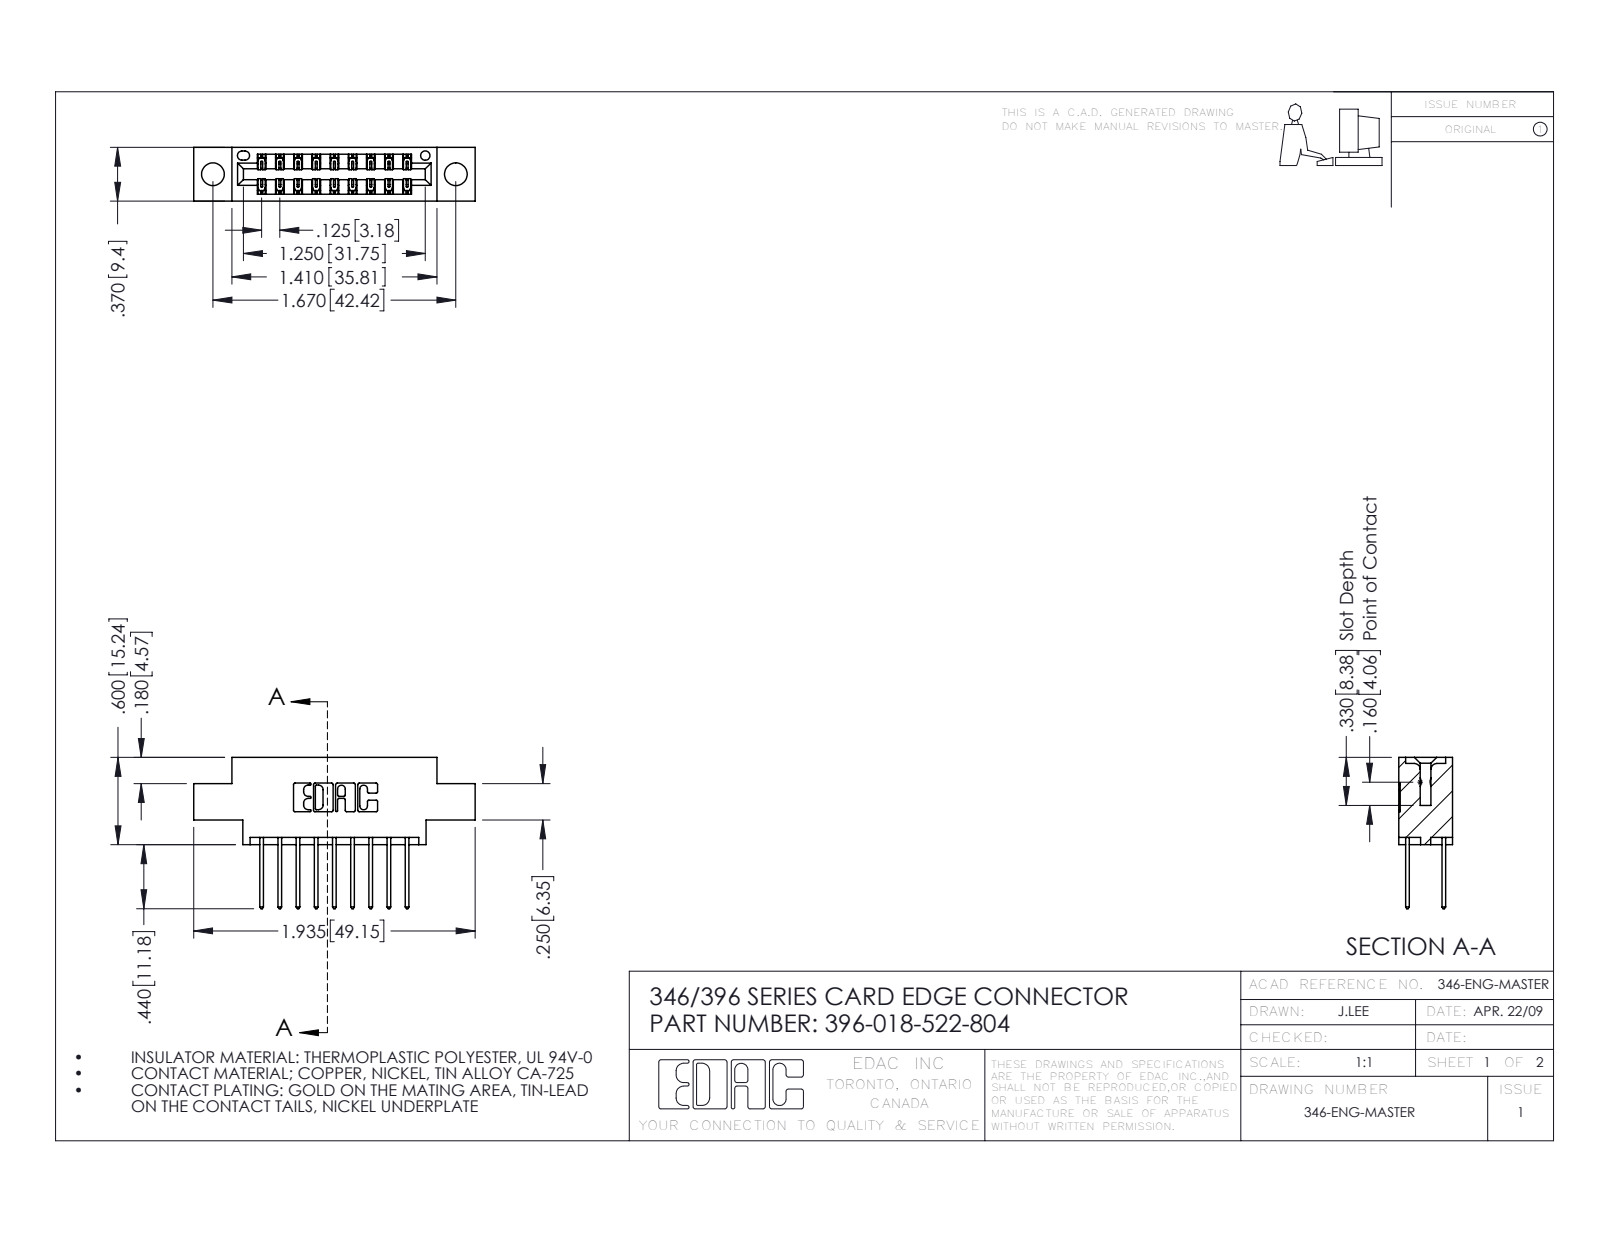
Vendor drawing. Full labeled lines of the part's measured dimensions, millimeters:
Part name (STEP PRODUCT): 345-292-001_345-293-122; 346 Part_0.170 Offset - 0.156 Dia-TH; 396-018-522-804
STEP written by: SolidWorks 2016 (CONFIG_CONTROL_DESIGN)
Units: millimetres
Bodies: 19 solids, 1062 faces (710 planar, 352 cylindrical, 0 other)
Overall size (bounding box): 49.1 × 26.4 × 9.4
Volume: 4 340 mm³ · Surface area: 5 654 mm²
Round holes (diameter × count): ⌀4 ×2, ⌀1.6 ×1
Partial cylindrical surfaces — rounded edges, fillets, slot ends (radius × count): R0.2 ×27, R0.3 ×22, R0.3 ×18, R0.2 ×6, R0.8 ×6, R0.7 ×3, R0.4 ×2, R0.6 ×2
Main face-to-face distances: 6.4, 1.2, 8.2, 9.4, 1.8, 7.6, 0.6, 7, 3.8, 5.6
Hole centre spacings: 6.2, 37.2, 42.4
